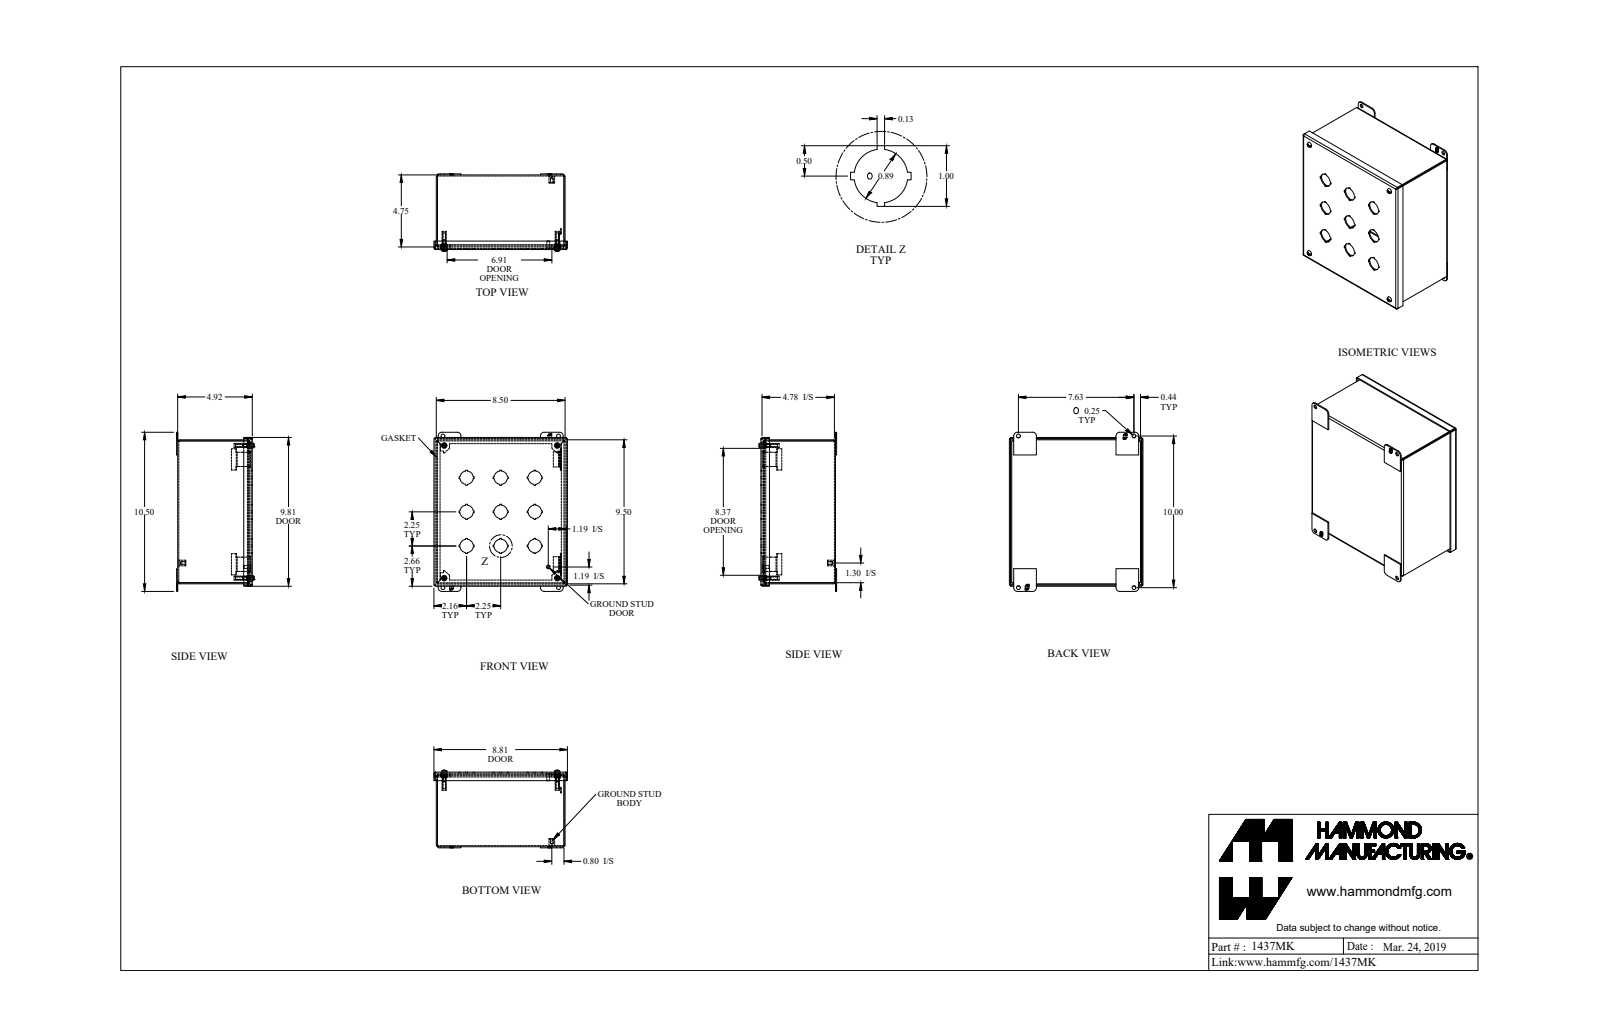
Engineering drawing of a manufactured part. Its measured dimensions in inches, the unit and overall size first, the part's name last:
Units: inches
Overall size (bounding box): 10.5 × 8.812 × 5.121
Round holes (diameter × count): ⌀0.886 ×9, ⌀0.25 ×8, ⌀0.159 ×4, ⌀0.406 ×4, ⌀0.156 ×1
Round bosses / shafts (diameter × count): ⌀0.39 ×4, ⌀0.275 ×4, ⌀0.19 ×4, ⌀0.148 ×4, ⌀0.375 ×1, ⌀0.25 ×1, ⌀0.188 ×1
Partial cylindrical surfaces — rounded edges, fillets, slot ends (radius × count): R0.036 ×12, R0.108 ×12, R0.25 ×8, R0.029 ×4, R0.086 ×4, R0.16 ×4, R0.171 ×4, R0.125 ×2
Main face-to-face distances: 0.072, 4.85, 4.922, 8.428, 4.778, 9.428, 8.5, 8.356, 9.5, 9.356
Hole centre spacings: 2.25, 3.182, 5.031, 4.5, 6.788, 8.75, 9.375, 8.924
Volume: 29.68 in³ · Surface area: 793.4 in²
Bodies: 23 solids, 859 faces (607 planar, 196 cylindrical, 56 other)
Part name (STEP PRODUCT): 1437MK_Default
STEP written by: SolidWorks 2019 (CONFIG_CONTROL_DESIGN)
